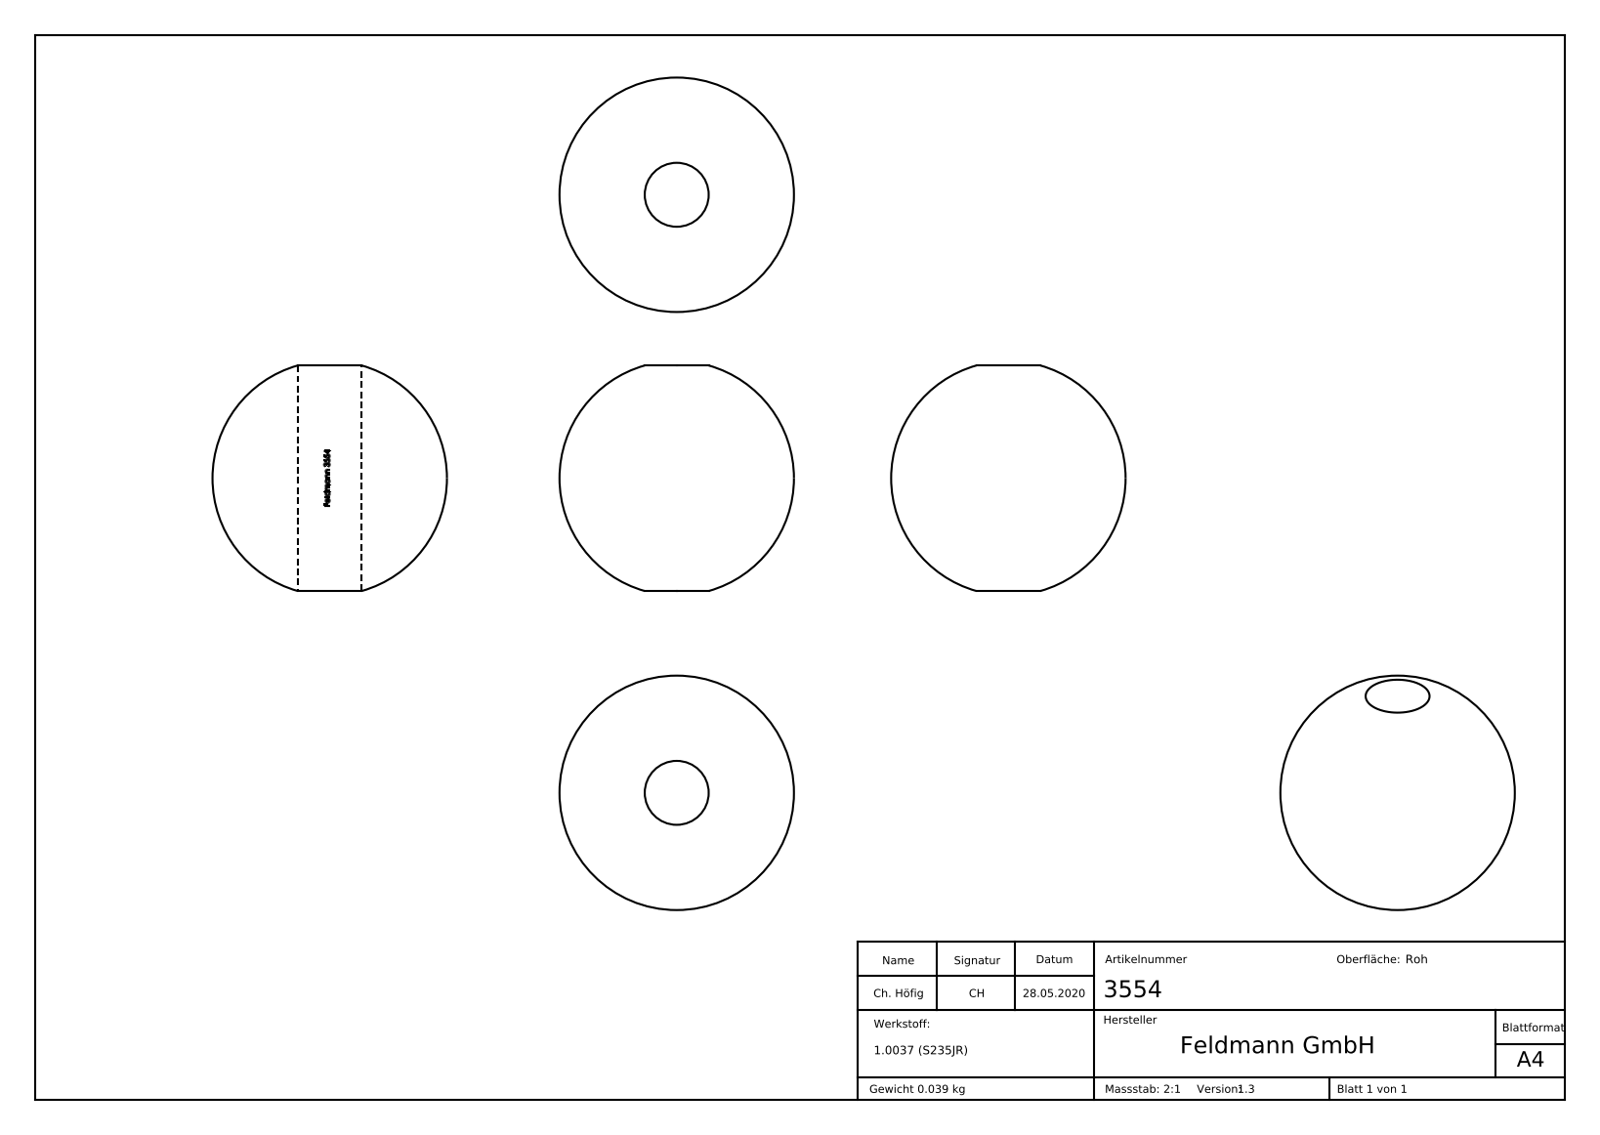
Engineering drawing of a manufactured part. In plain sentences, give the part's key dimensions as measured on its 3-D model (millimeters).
The part is named "3554". Its 3-D file was written by "SolidWorks 2015 (CONFIG_CONTROL_DESIGN)". It is 1 solid with 178 faces: 82 planar, 17 cylindrical and 79 other. Overall it measures 22 by 22 by 21.17 millimeters. Its volume is 4 965 cubic millimeters and its surface area 1 865 square millimeters. Round holes: 1 of diameter 6. Partial cylindrical surfaces (rounded edges, fillets, slot ends): 1 of radius 3.1. The main face-to-face distances are 0.45, 0.55, 0.5, 0.35, 0.53, 0.81, 1.79, 4.38, 1.84, 1.19.
